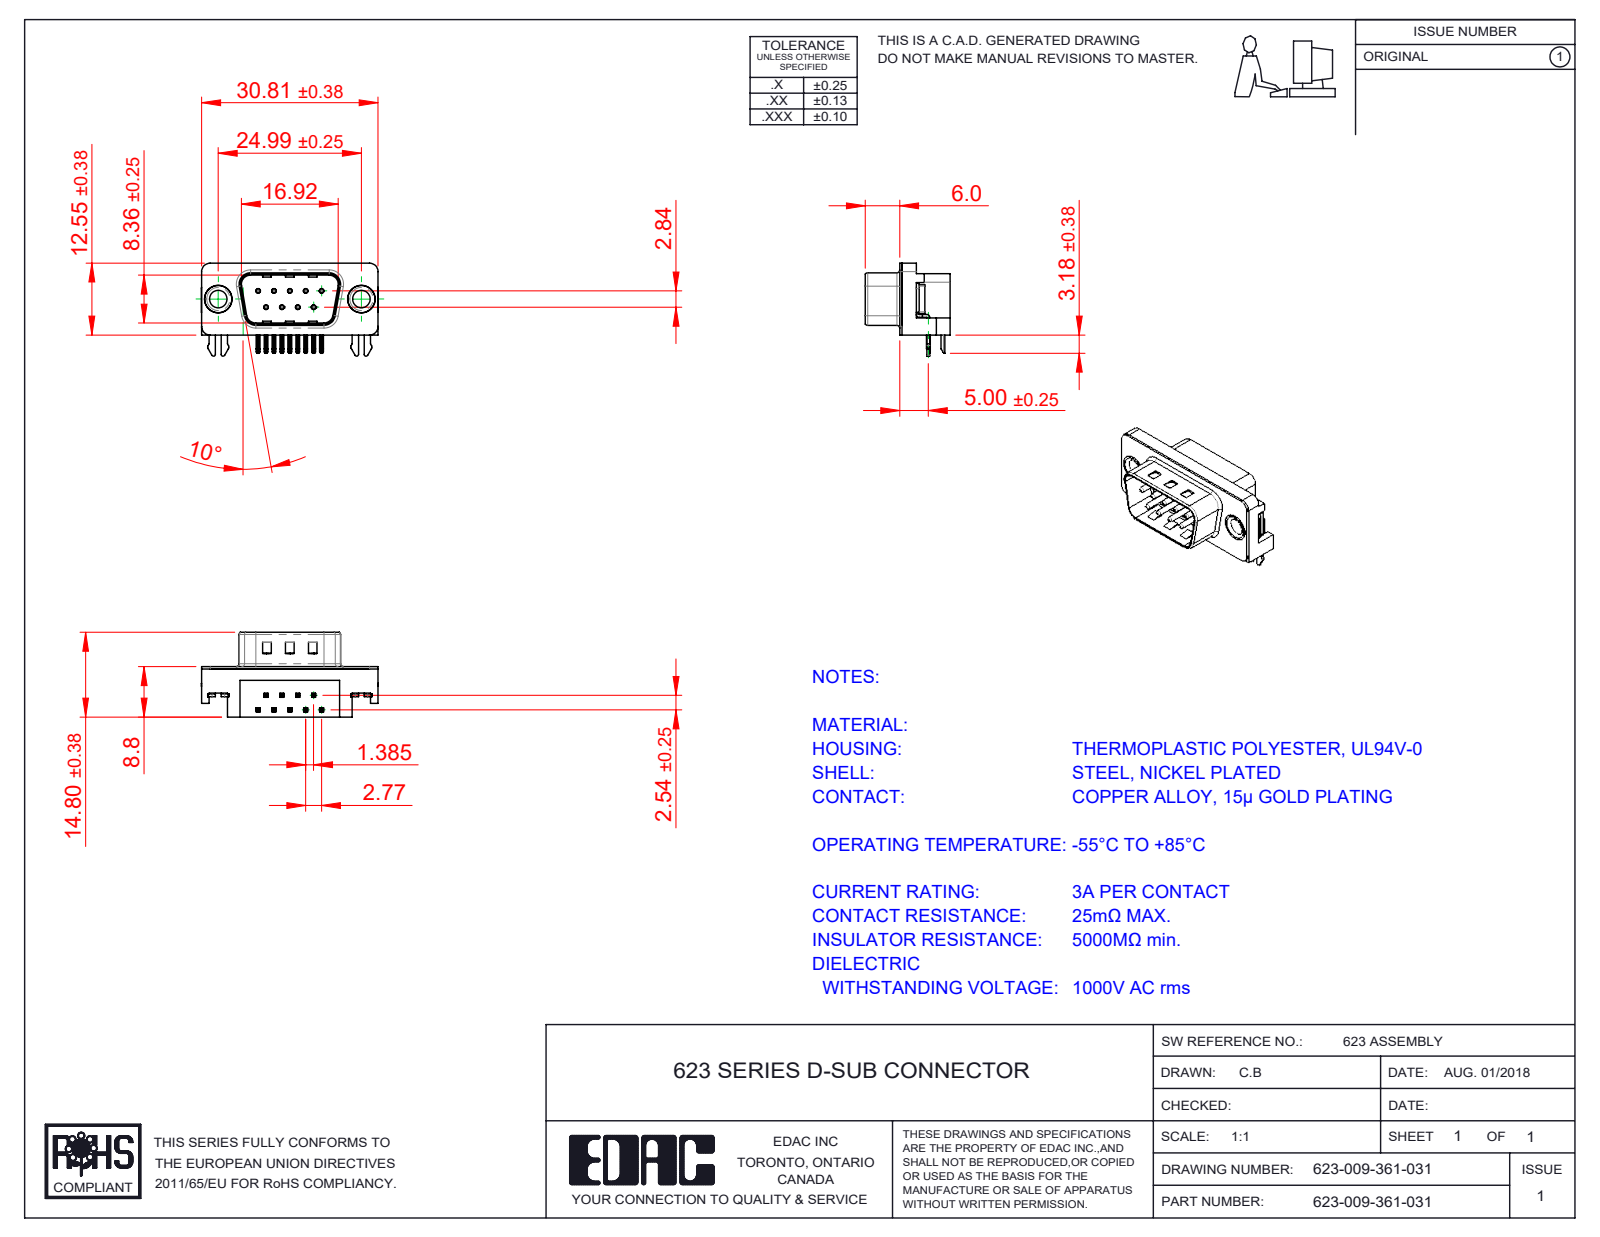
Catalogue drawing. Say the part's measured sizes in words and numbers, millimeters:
The part is named "623 Thru Hole Rivet; 623-009-361-031; 623 2 Prong Board Lock; 623 Contact Top (+3 more)". Its 3-D file was written by "SolidWorks 2016 (CONFIG_CONTROL_DESIGN)". It is 15 solids with 973 faces: 601 planar, 291 cylindrical and 81 other. Overall it measures 30.89 by 16.25 by 14.8 millimeters. Its volume is 2 464 cubic millimeters and its surface area 3 814 square millimeters. Round holes: 9 of diameter 0.35, 9 of diameter 0.8, 2 of diameter 3.05, 2 of diameter 4, 2 of diameter 4.8, 2 of diameter 5. Round bosses or shafts: 9 of diameter 0.75, 2 of diameter 4.9, 2 of diameter 4.75, 2 of diameter 3.85. Partial cylindrical surfaces (rounded edges, fillets, slot ends): 44 of radius 0.25, 18 of radius 0.12, 14 of radius 0.5, 8 of radius 1, 8 of radius 1.5, 4 of radius 0.32, 4 of radius 0.9, 4 of radius 1.6. The main face-to-face distances are 0.4, 8.4, 8.8, 5.9, 2.9, 2.5, 0.35, 8.76, 10.69, 10.34. The hole center spacings are 3.16, 2.77, 5.54, 5.03, 5.04, 8.31, 7.48, 7.49.
